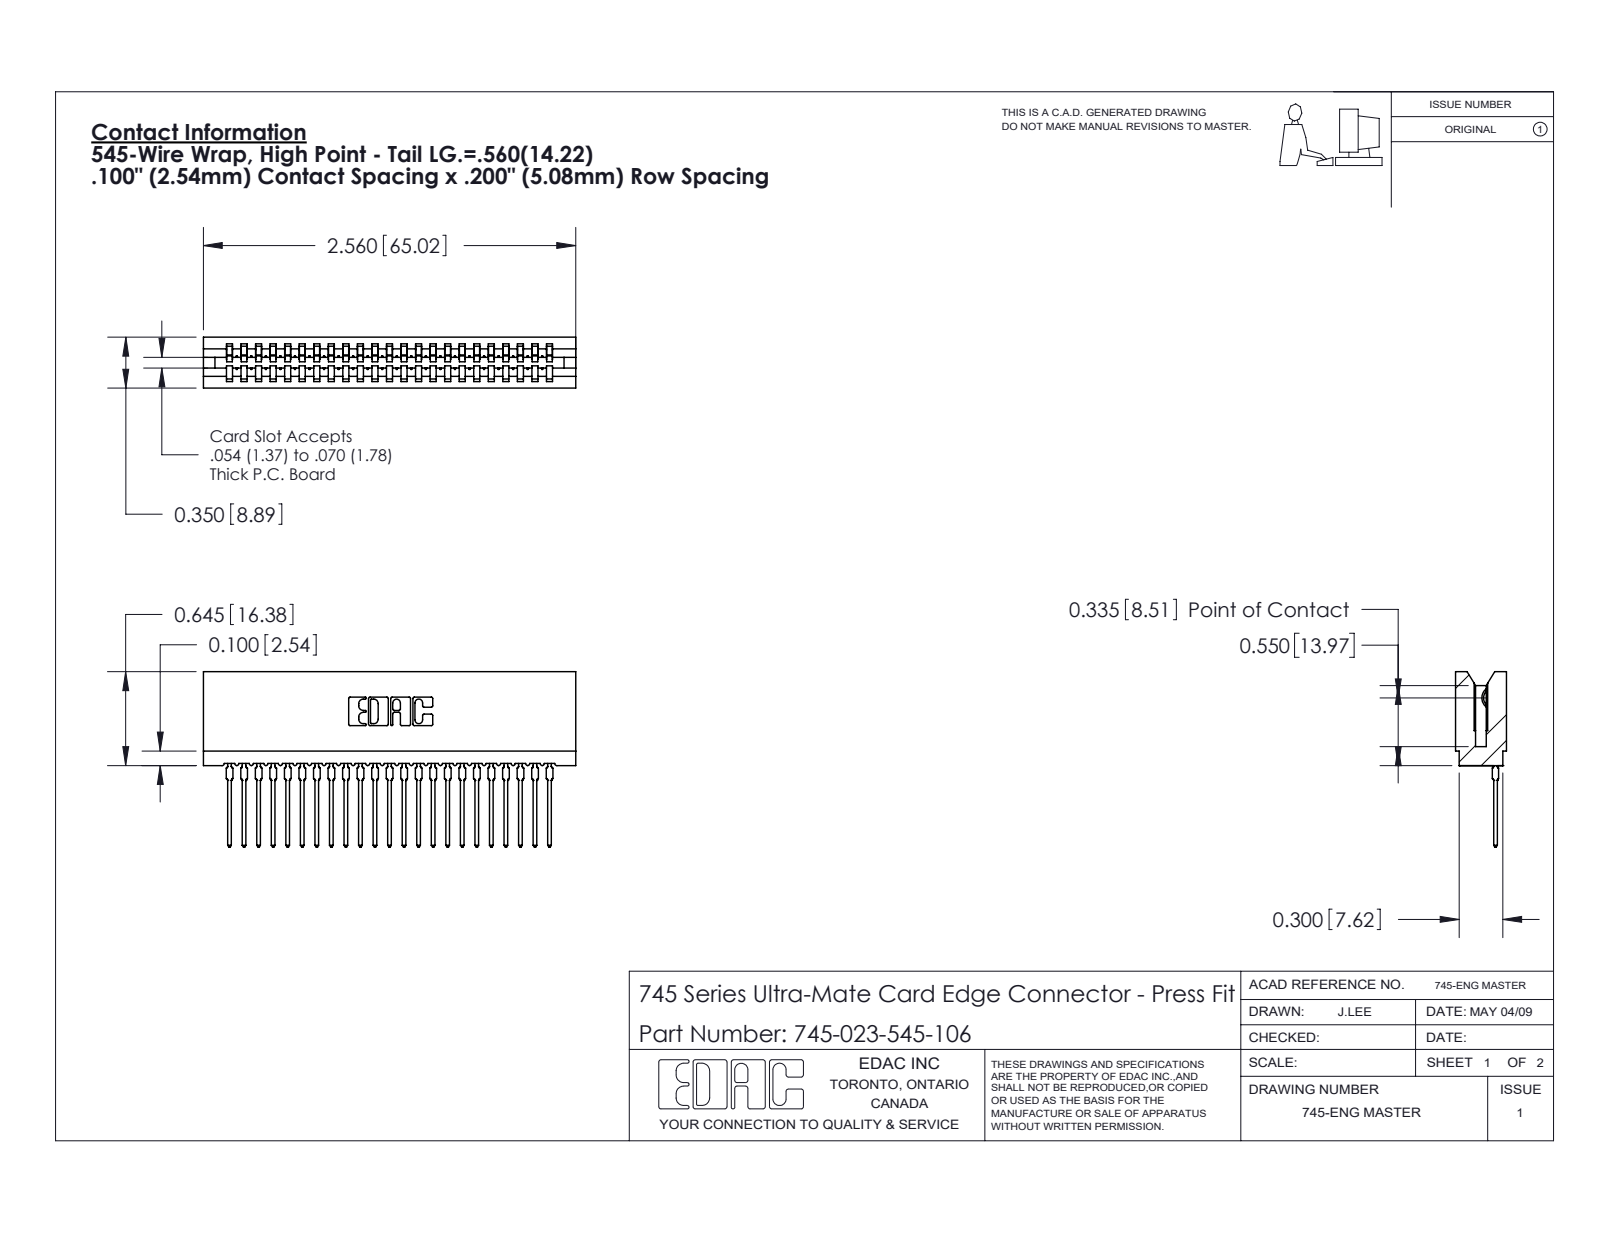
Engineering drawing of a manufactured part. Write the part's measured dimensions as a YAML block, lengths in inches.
part_name: "745 Part_Insulator Option - 06; 745-292-001_545; 745-023-545-106"
step_written_by: "SolidWorks 2020 (CONFIG_CONTROL_DESIGN)"
units: inches
bodies: {solids: 24, faces: 2672, planar: 1597, cylindrical: 477, other: 598}
overall_size: [2.56, 1.206, 0.35]
volume: 0.354
surface_area: 16.74
partial_cylinders:
  - {radius: 0.015, count: 46}
  - {radius: 0.021, count: 46}
  - {radius: 0.01, count: 22}
  - {radius: 0.007, count: 6}
  - {radius: 0.031, count: 6}
  - {radius: 0.005, count: 4}
  - {radius: 0.011, count: 4}
  - {radius: 0.026, count: 3}
face_to_face_distances: [0.1, 0.2, 0.35, 0.3, 0.138, 0.212, 0.045, 0.305, 0.093, 0.167]
